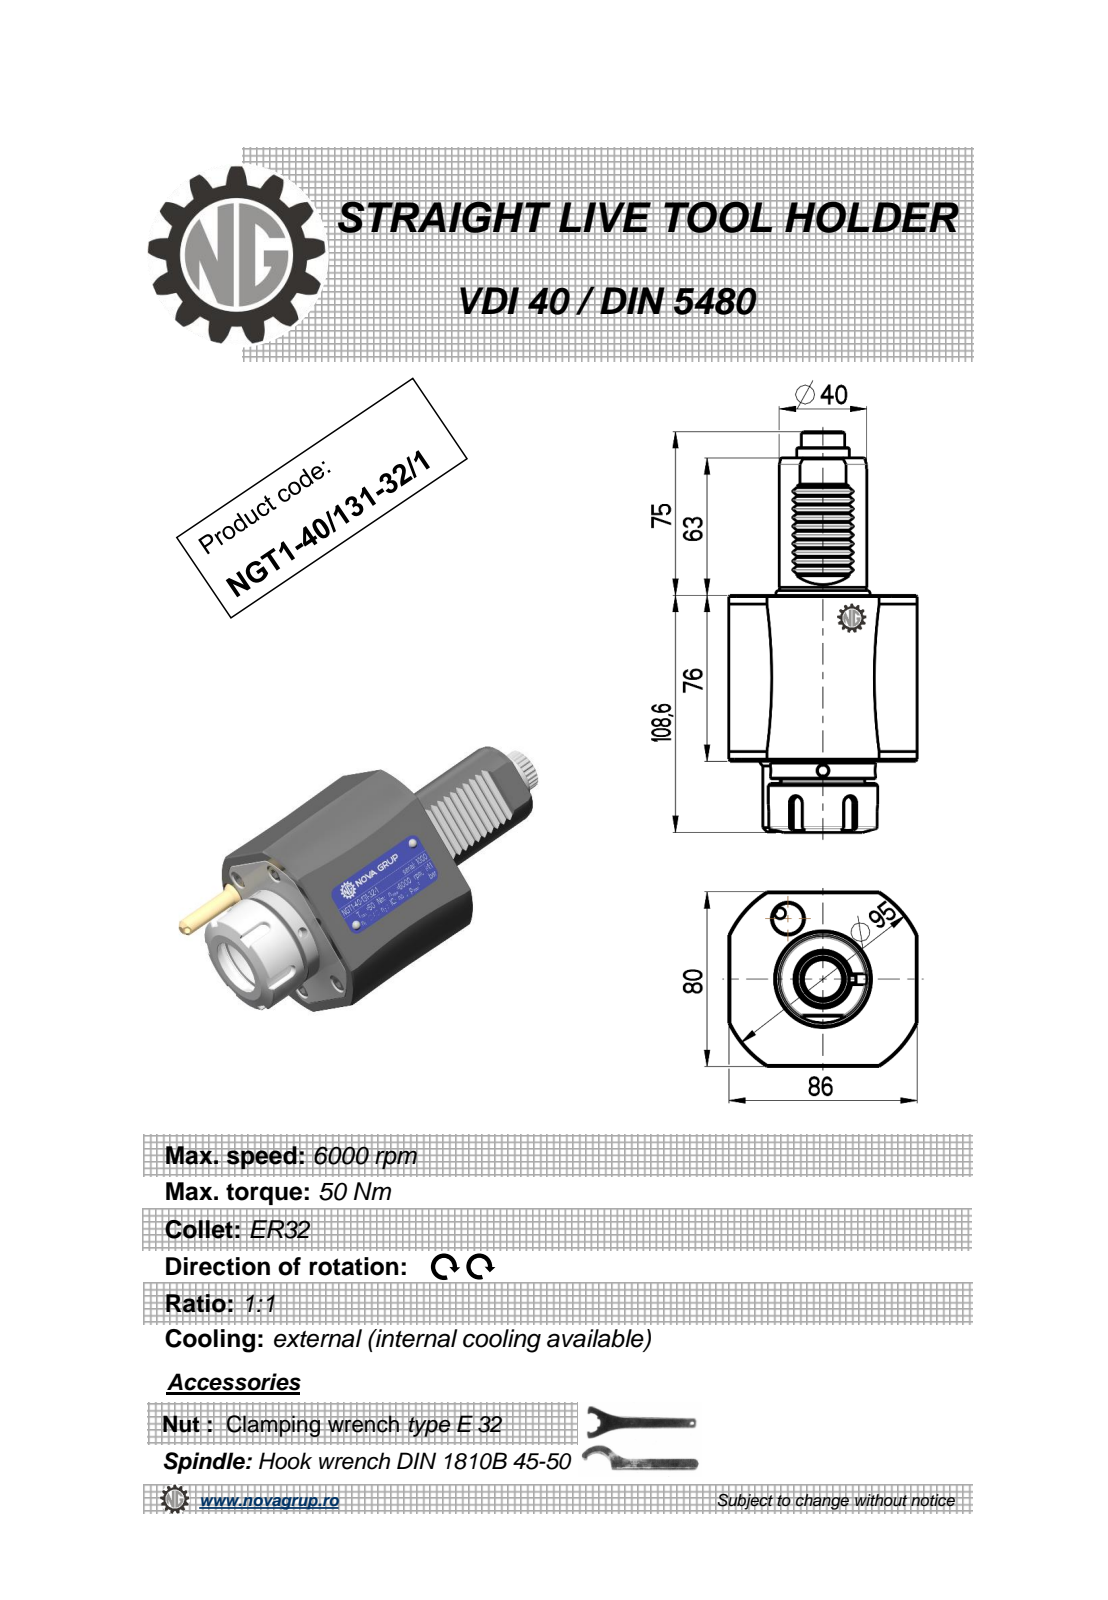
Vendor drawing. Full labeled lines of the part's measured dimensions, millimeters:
Part name (STEP PRODUCT): NGT1_40_131_32_1
STEP written by: PRO/ENGINEER BY PARAMETRIC TECHNOLOGY CORPORATION, 2010280 (CONFIG_CONTROL_DESIGN)
Units: millimetres
Bodies: 1 solid, 379 faces (107 planar, 162 cylindrical, 110 other)
Overall size (bounding box): 183.6 × 86 × 80
Volume: 610 536 mm³ · Surface area: 53 363 mm²
Round holes (diameter × count): ⌀5 ×3, ⌀3 ×1, ⌀27 ×1
Round bosses / shafts (diameter × count): ⌀50 ×1, ⌀48 ×1, ⌀41.5 ×1, ⌀41 ×1, ⌀40 ×1, ⌀28.46 ×1, ⌀24 ×1, ⌀8 ×1
Partial cylindrical surfaces — rounded edges, fillets, slot ends (radius × count): R2.08 ×48, R0.3 ×10, R0.22 ×6, R3 ×5, R9.08 ×1, R9.92 ×1, R15 ×1, R47.5 ×1
Main face-to-face distances: 76, 80, 86, 2.83, 104.1, 28.1, 5.66, 63, 139, 167.1
Hole centre spacings: 40
